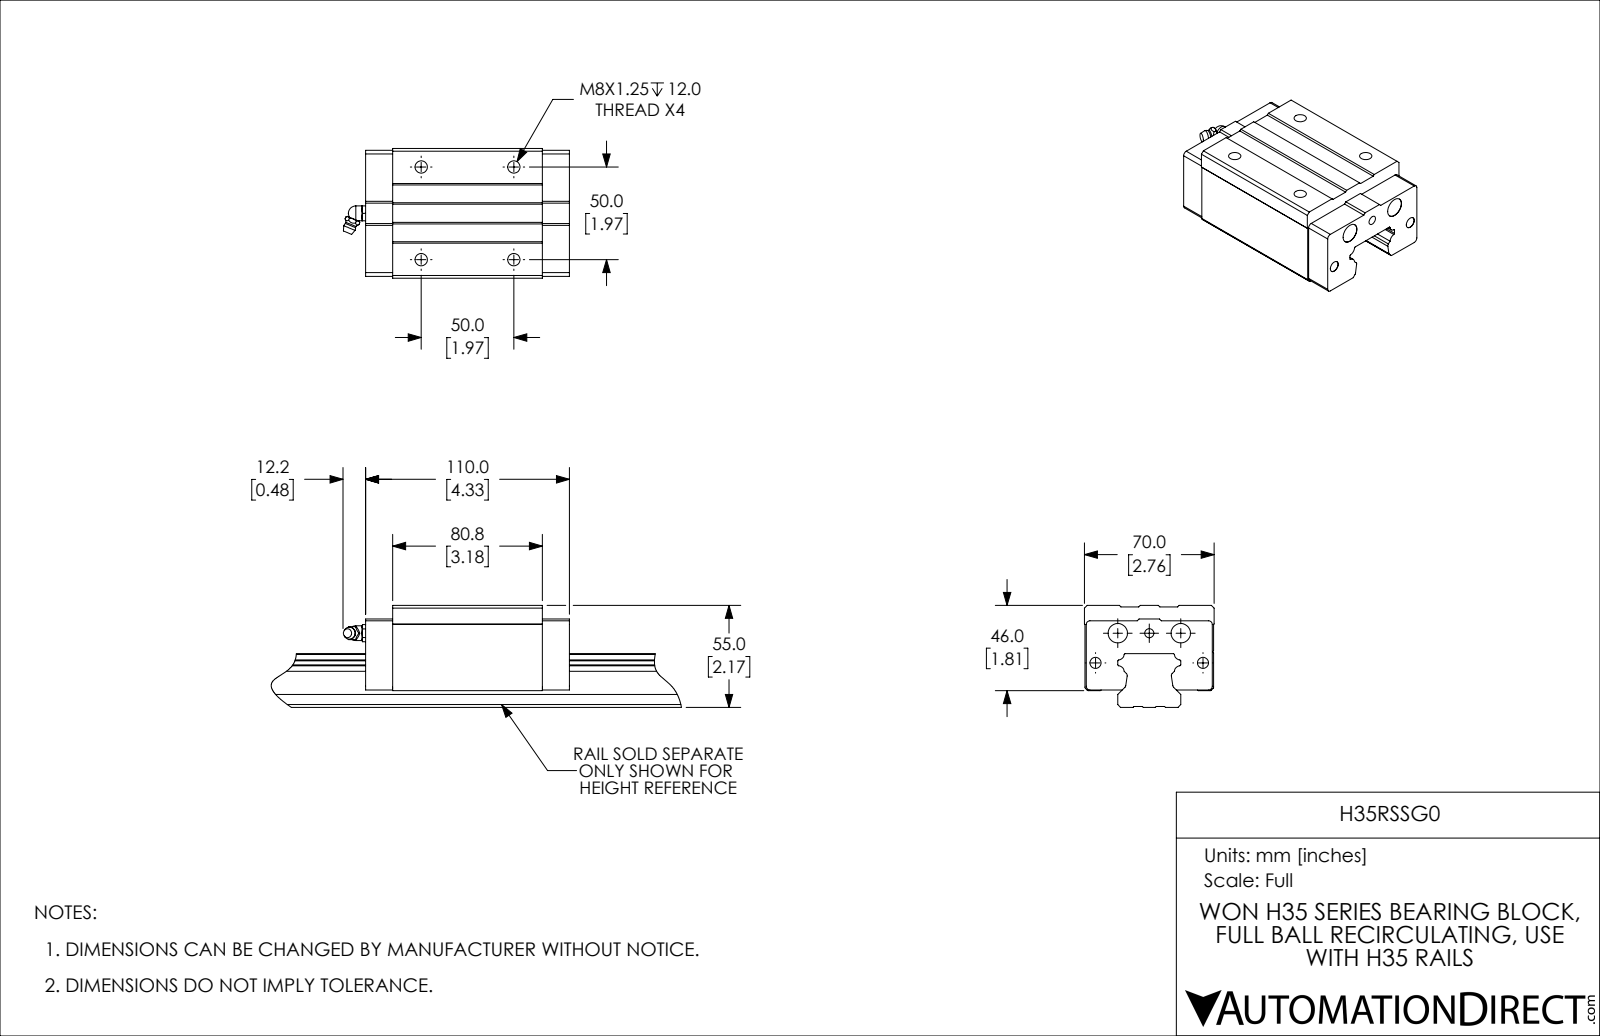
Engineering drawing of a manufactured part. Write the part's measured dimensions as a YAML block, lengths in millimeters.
part_name: "H35RSSG0"
step_written_by: "SolidWorks 2019 (CONFIG_CONTROL_DESIGN)"
units: millimeters
bodies: {solids: 2, faces: 170, planar: 85, cylindrical: 55, other: 30}
overall_size: [122, 70, 46]
volume: 268414
surface_area: 36789
round_holes:
  - {diameter: 6.65, count: 4}
  - {diameter: 6, count: 2}
  - {diameter: 10.5, count: 2}
  - {diameter: 4.92, count: 1}
round_bosses_or_shafts:
  - {diameter: 8, count: 1}
  - {diameter: 6, count: 1}
partial_cylinders:
  - {radius: 1, count: 4}
  - {radius: 1.5, count: 4}
  - {radius: 2, count: 4}
  - {radius: 3.2, count: 4}
  - {radius: 0.5, count: 2}
  - {radius: 1.3, count: 1}
face_to_face_distances: [45.6, 26, 19.6, 69.4, 17.7, 0.7, 68.7, 110, 1, 44.8]
hole_center_spacings: [50, 17, 20, 33.12, 48.7, 70.71, 34, 58]
